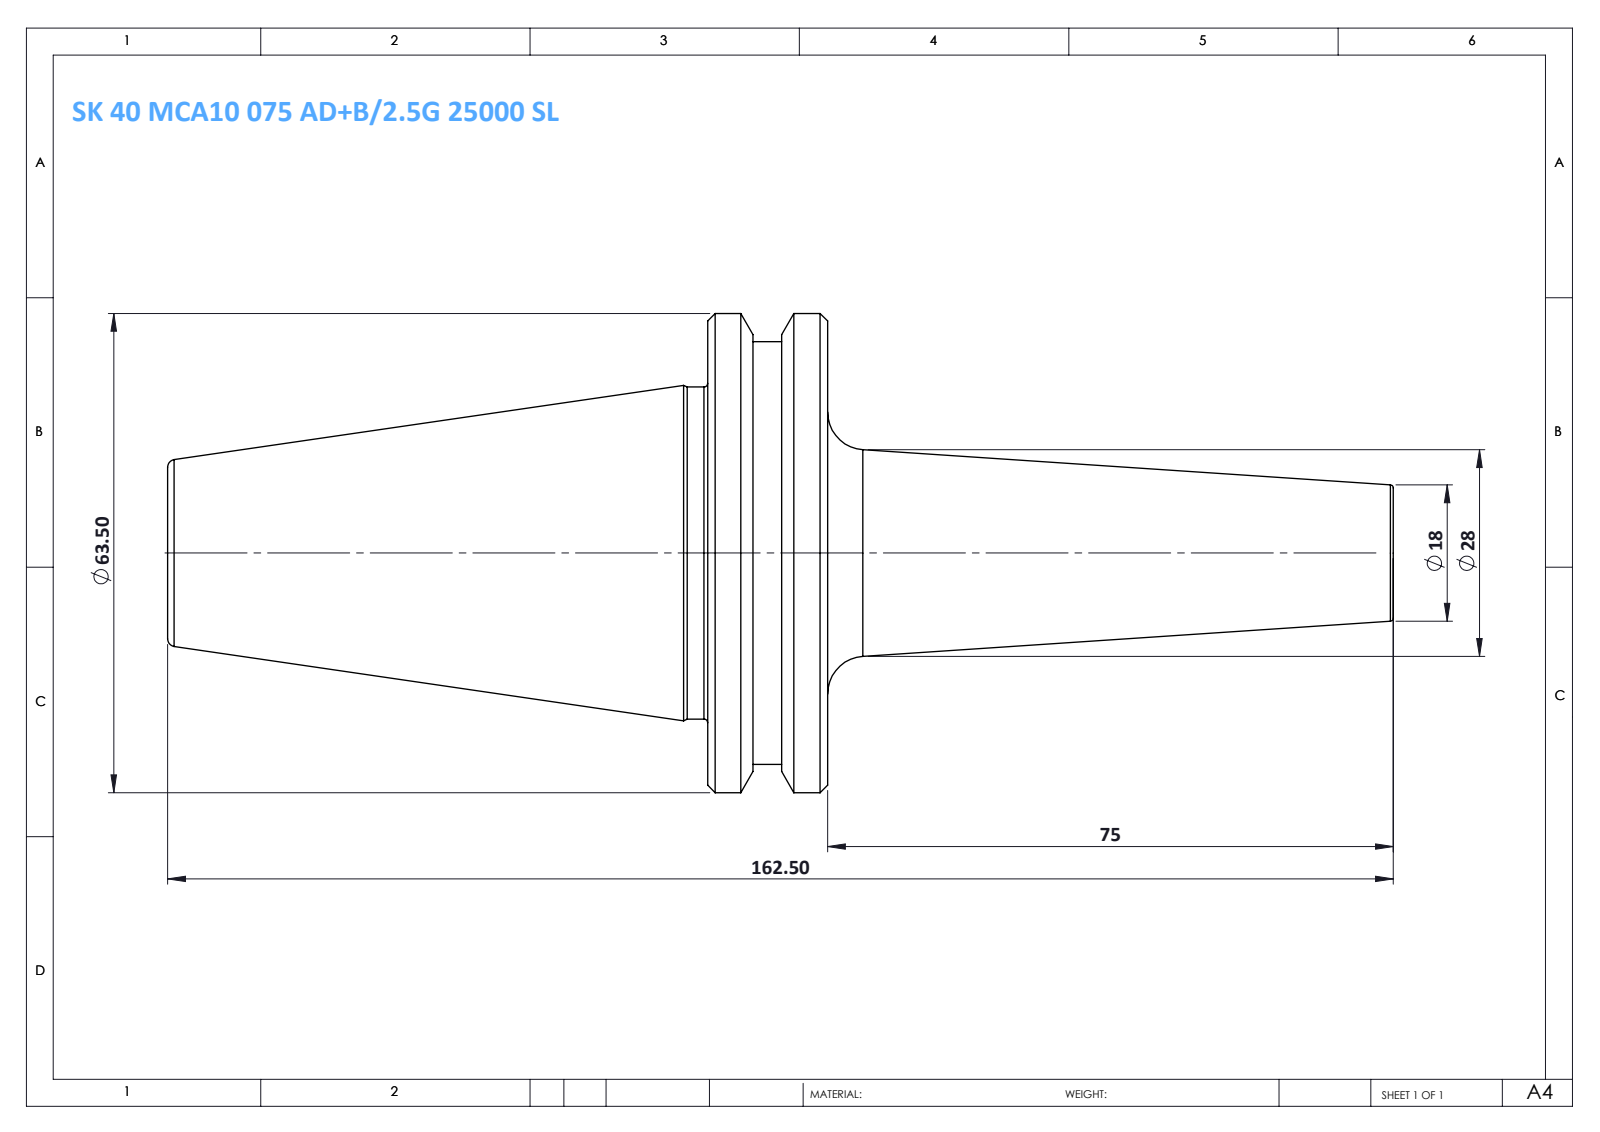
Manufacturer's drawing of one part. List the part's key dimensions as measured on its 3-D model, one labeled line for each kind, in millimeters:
Part name (STEP PRODUCT): SK40 MCA10 075 AD+B -2.5G 25000 SL
STEP written by: SolidWorks 2014 (CONFIG_CONTROL_DESIGN)
Units: millimetres
Bodies: 1 solid, 36 faces (6 planar, 8 cylindrical, 22 other)
Overall size (bounding box): 162.5 × 63.5 × 63.5
Volume: 149 188 mm³ · Surface area: 21 852 mm²
Round bosses / shafts (diameter × count): ⌀63.5 ×1, ⌀56 ×1, ⌀44 ×1
Main face-to-face distances: 15.9, 87.5, 71.6, 75, 90.9, 162.5, 81.1, 6.1, 9.8, 81.4
